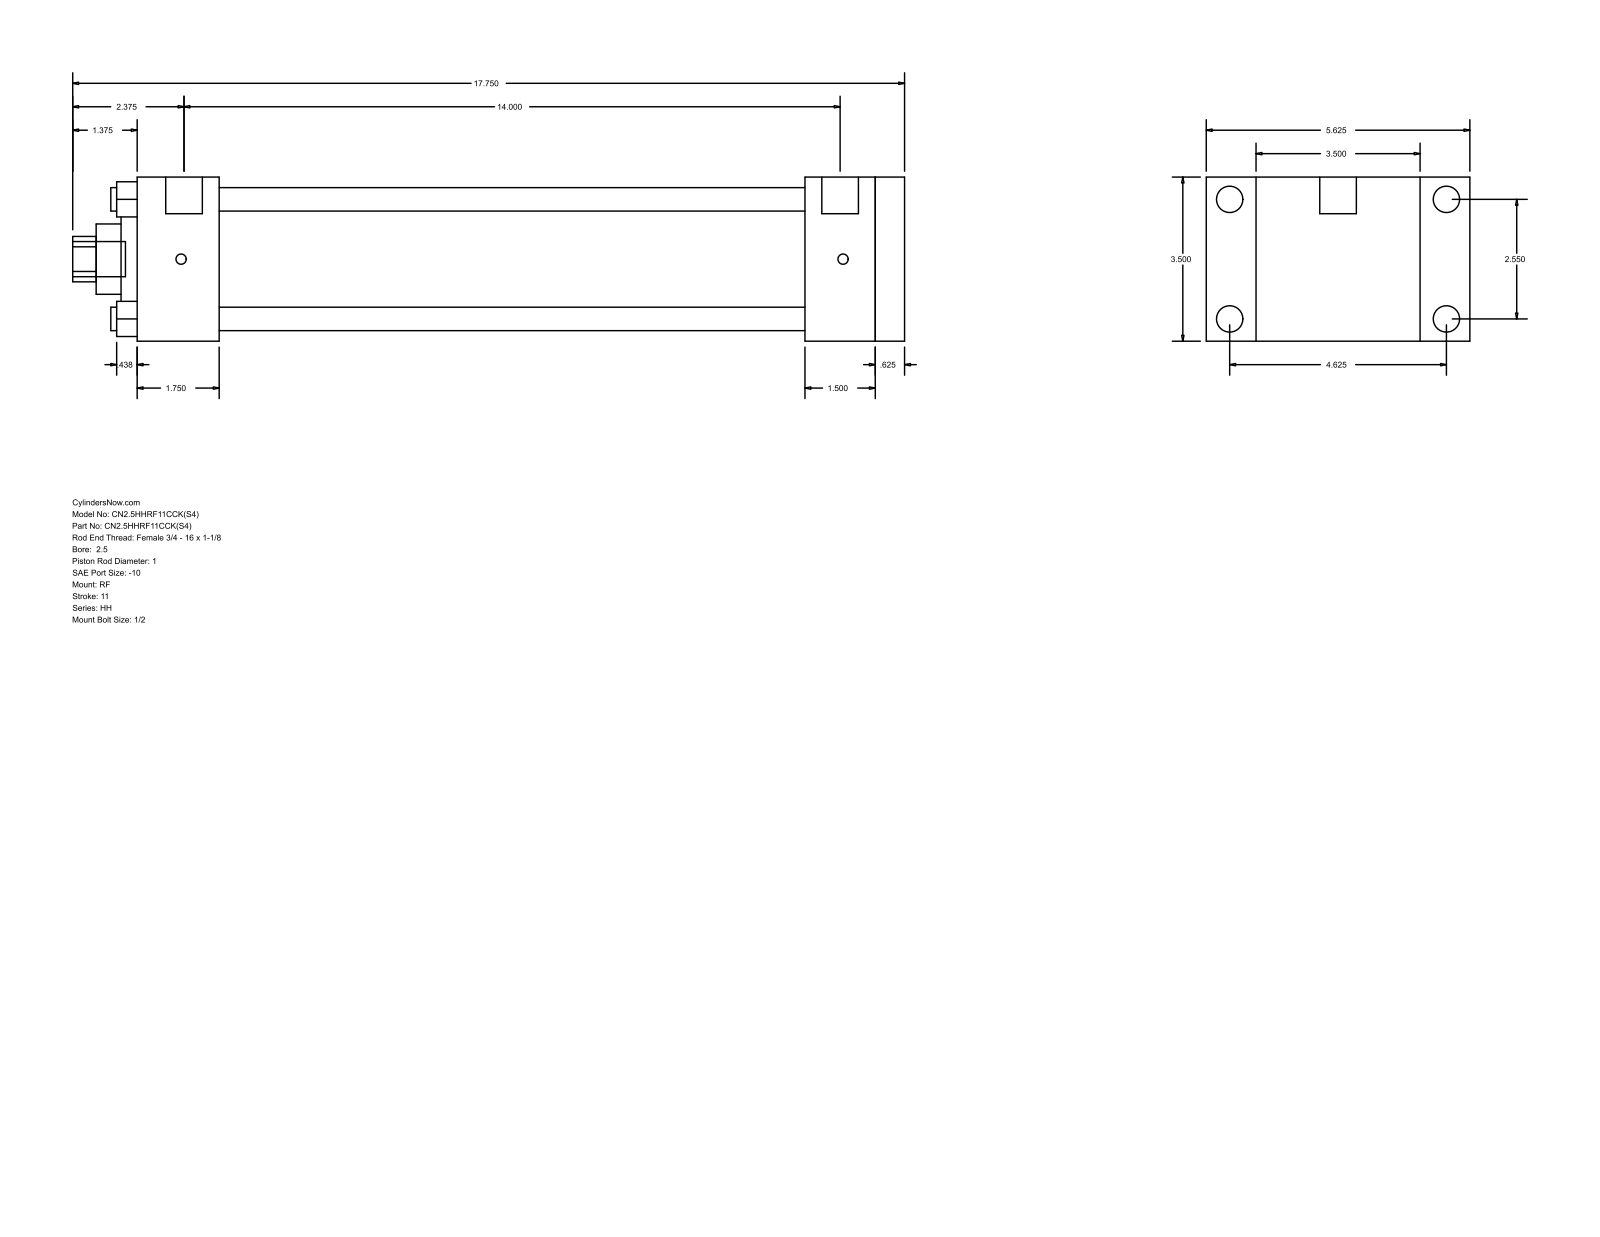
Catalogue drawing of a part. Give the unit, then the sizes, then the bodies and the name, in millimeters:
Units: millimetres
Overall size (bounding box): 450.85 × 142.88 × 88.9
Round holes (diameter × count): ⌀12.7 ×4, ⌀25.4 ×1, ⌀38.1 ×1, ⌀60.33 ×1, ⌀73.03 ×1
Round bosses / shafts (diameter × count): ⌀14.3 ×4, ⌀5.56 ×4, ⌀19.84 ×2, ⌀19.05 ×1
Partial cylindrical surfaces — rounded edges, fillets, slot ends (radius × count): R12.29 ×1
Main face-to-face distances: 88.9, 15.87, 400.06, 415.93, 44.46, 355.6, 371.47, 361.96, 317.5, 38.1
Hole centre spacings: 45.79, 64.76, 91.58
Bodies: 0 solids, 94 faces (65 planar, 29 cylindrical, 0 other)
Part name (STEP PRODUCT): HH_RF__0250_1
STEP written by: GSSL Pune (CONFIG_CONTROL_DESIGN)
